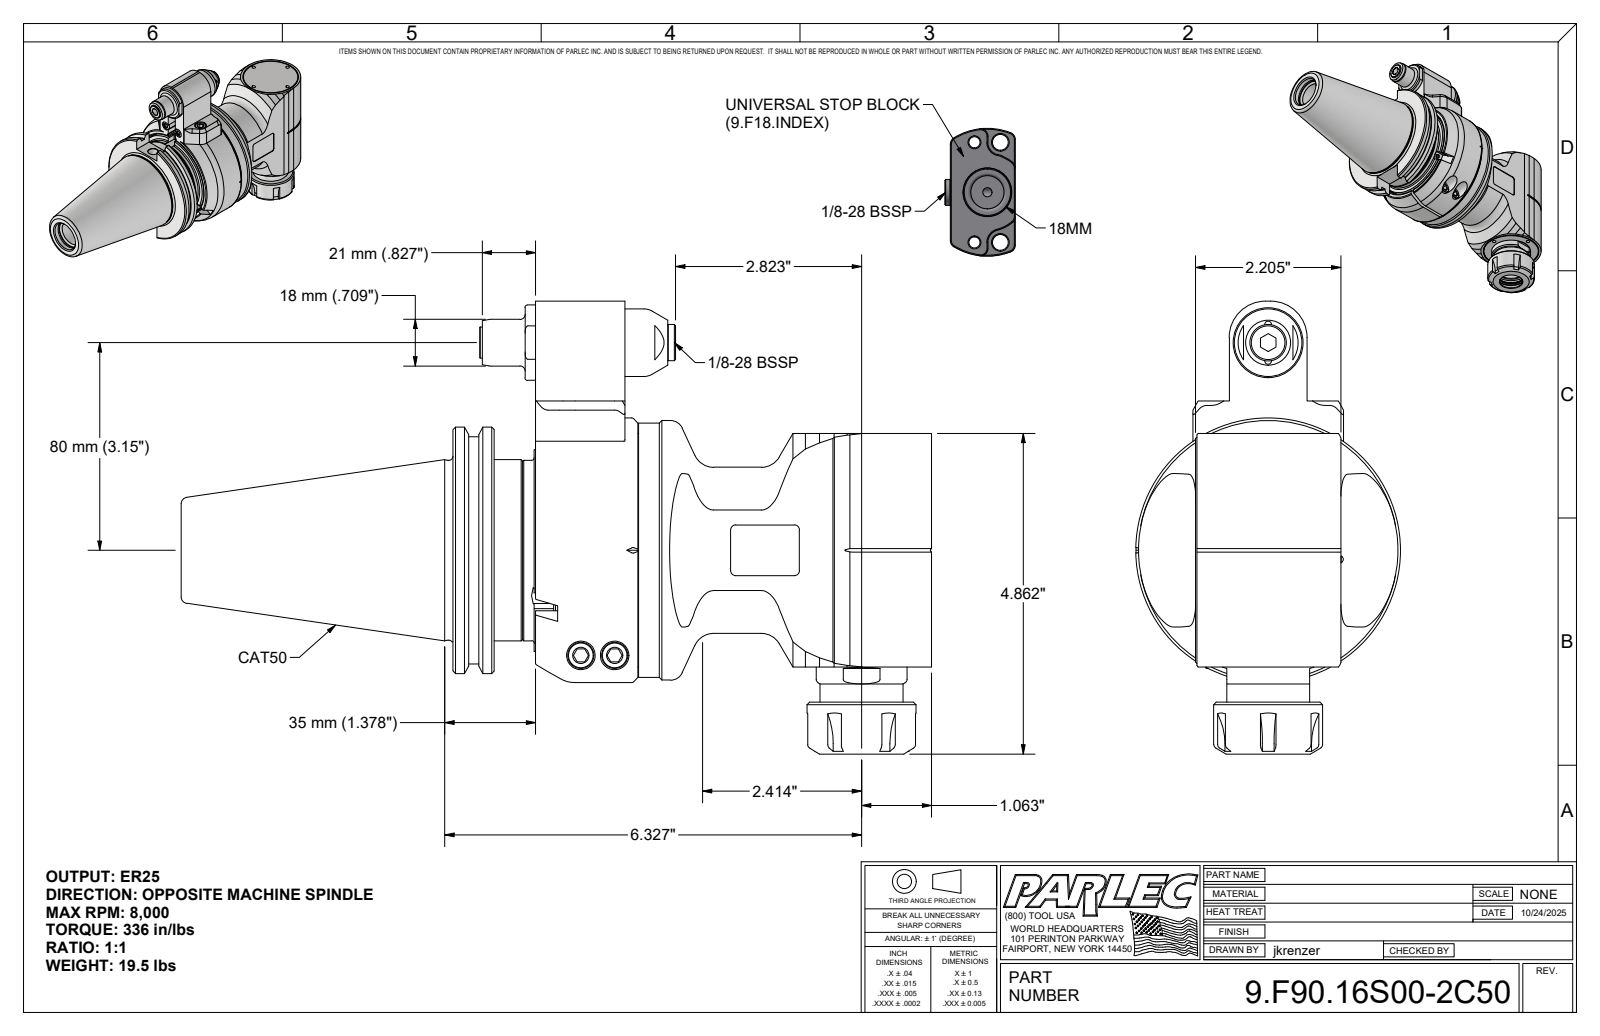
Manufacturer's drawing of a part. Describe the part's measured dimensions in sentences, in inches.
The part is named "9.F90.16S00-2C50; 9_F90_16S00; 9GA11C_458". Its 3-D file was written by "Autodesk Inventor 2025 (AUTOMOTIVE_DESIGN)". It is 4 solids with 613 faces: 278 planar, 160 cylindrical and 175 other. Overall it measures 11.39 by 6.87 by 4.016 inches. Its volume is 77.75 cubic inches and its surface area 257.3 square inches. Round holes: 4 of diameter 0.126, 3 of diameter 0.256, 2 of diameter 0.102, 2 of diameter 0.13, 2 of diameter 0.165, 2 of diameter 0.197, 2 of diameter 0.315, 2 of diameter 0.409, 2 of diameter 0.433, 2 of diameter 0.492, 2 of diameter 1.063, 1 of diameter 0.098. Round bosses or shafts: 4 of diameter 0.394, 2 of diameter 0.709, 2 of diameter 0.472, 2 of diameter 0.315, 2 of diameter 0.236, 2 of diameter 0.098, 1 of diameter 4.016, 1 of diameter 3.937. Partial cylindrical surfaces (rounded edges, fillets, slot ends): 14 of radius 0.039, 12 of radius 0.079, 6 of radius 0.118, 6 of radius 0.984, 4 of radius 0.157, 2 of radius 0.016, 2 of radius 0.02, 2 of radius 0.315. The main face-to-face distances are 1.28, 1.252, 0.028, 2.183, 0.931, 0.904, 2.808, 1.556, 1.529, 0.625. The hole center spacings are 0.846, 1.197, 0.276, 0.959, 1.222, 1.49, 1.693, 1.994.
